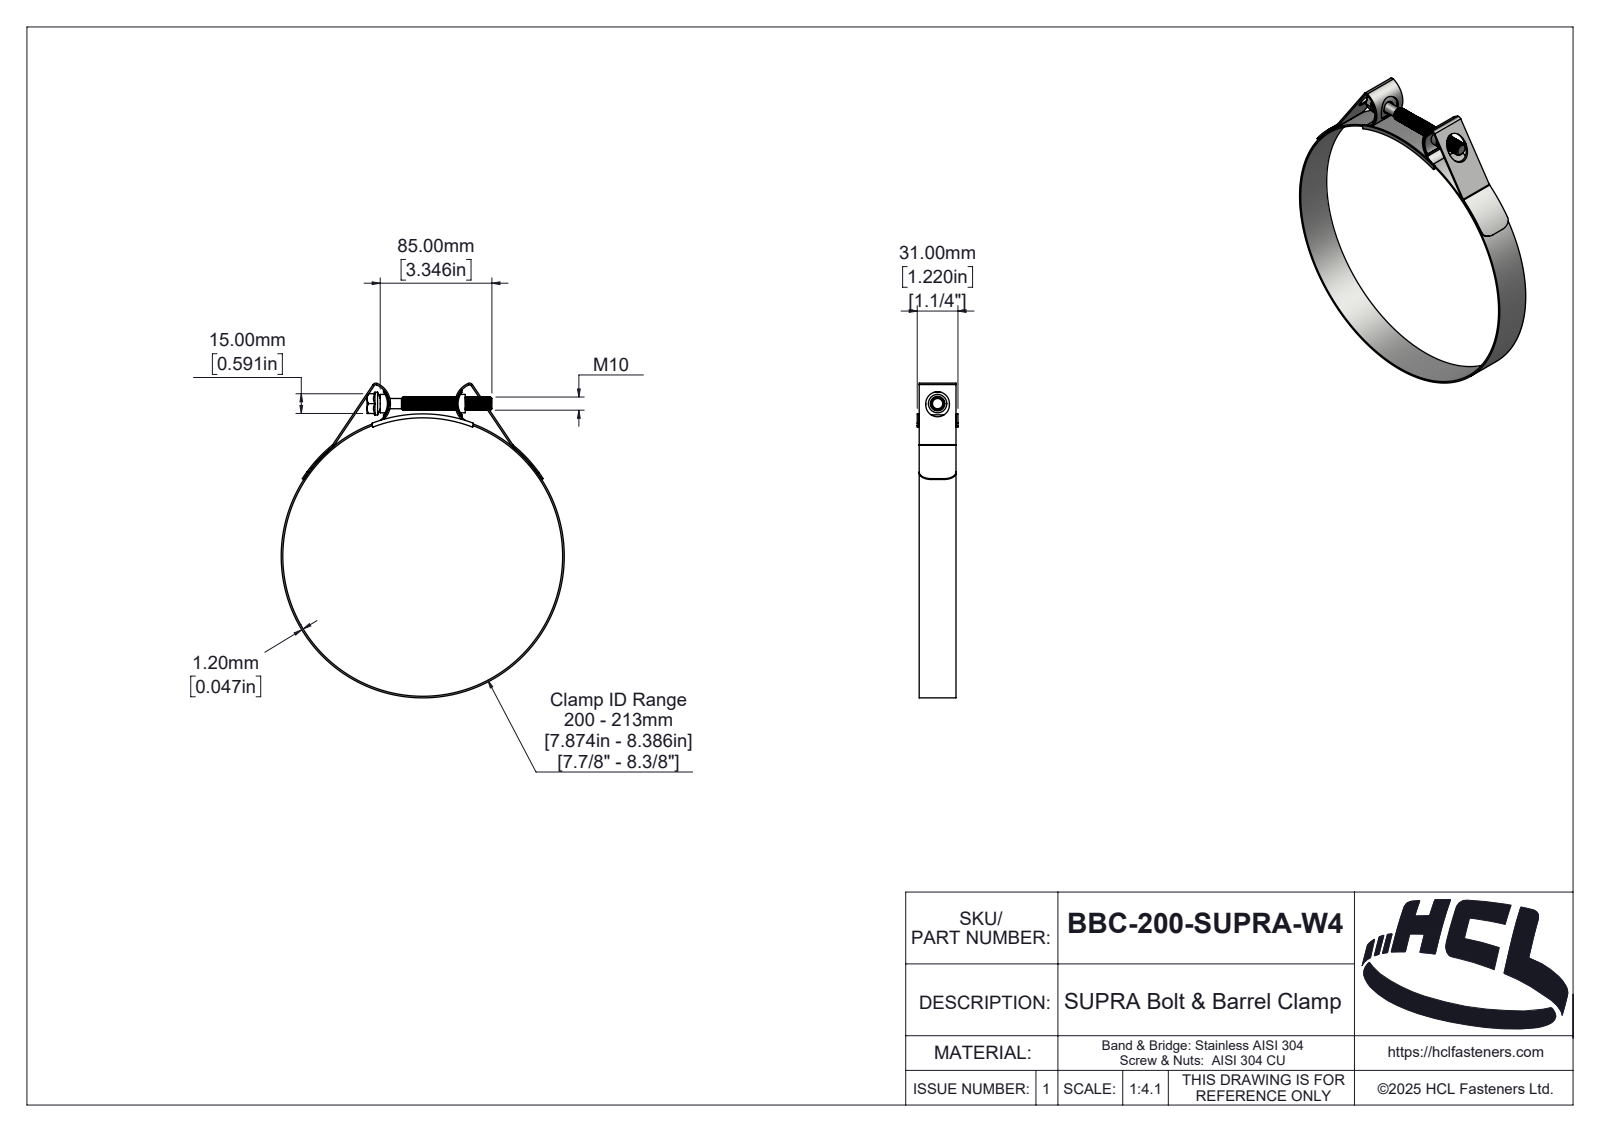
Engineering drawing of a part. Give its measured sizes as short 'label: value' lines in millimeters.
name: BBC-200-SUPRA-W4
written by: SolidWorks 2025 (AUTOMOTIVE_DESIGN)
unit: mm
bodies: 5 solids, 382 faces (50 planar, 246 cylindrical, 86 other)
size: 239.4 × 215.4 × 31
volume: 39 886 mm³; area: 61 441 mm²
holes: 1× ⌀213
bosses: 1× ⌀215.4, 1× ⌀17.32, 1× ⌀14, 1× ⌀10, 1× ⌀7.8
rounds: 4× R1, 2× R1.3, 2× R2, 2× R2.5, 2× R3.2, 2× R9, 2× R14.44, 2× R15.44
face distances: 1.2, 28, 29.5, 1.5, 29.8, 28.3, 31, 28.6, 2.5, 62.2
